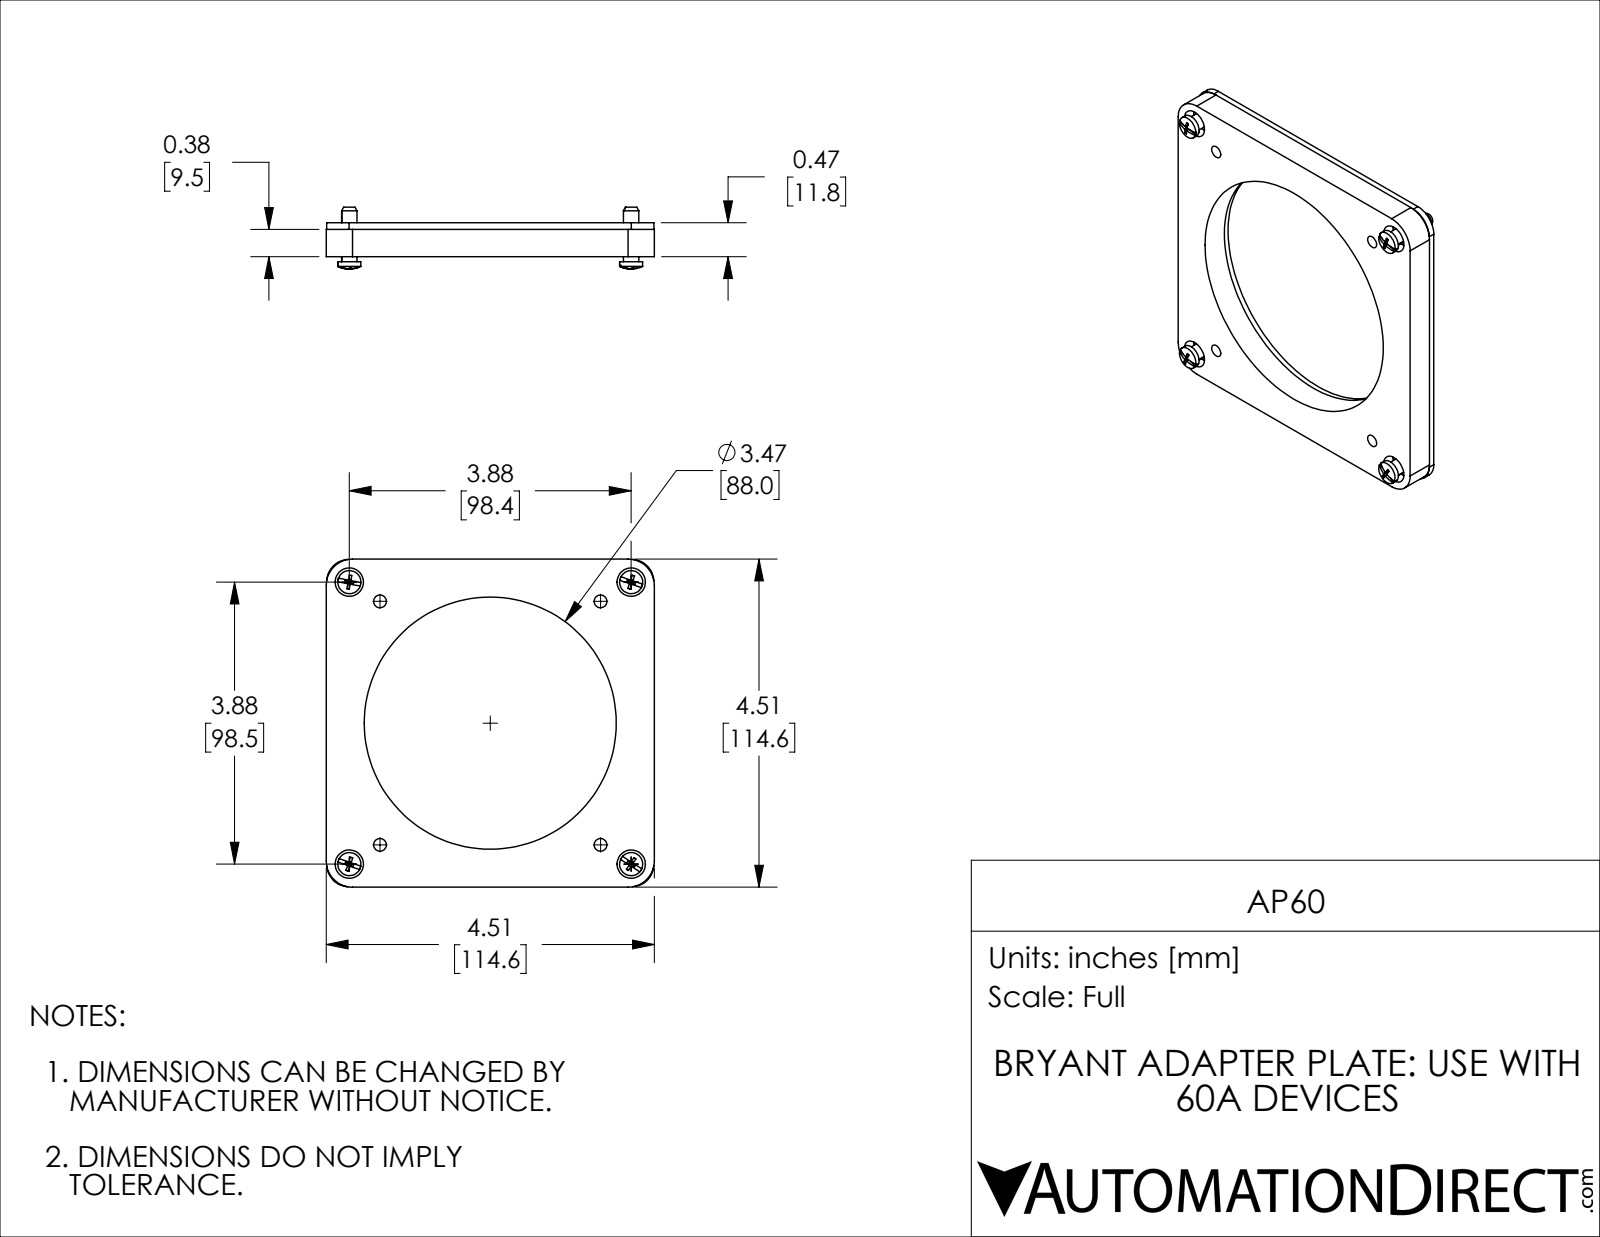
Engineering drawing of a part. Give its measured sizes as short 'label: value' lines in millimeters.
name: AP60
written by: SolidWorks 2021 (CONFIG_CONTROL_DESIGN)
unit: mm
bodies: 6 solids, 188 faces (100 planar, 72 cylindrical, 16 other)
size: 114.55 × 114.55 × 21.51
volume: 81 078 mm³; area: 39 036 mm²
holes: 8× ⌀5.49, 4× ⌀5.56, 4× ⌀9.91, 2× ⌀4.44, 2× ⌀4.45, 1× ⌀88.01, 1× ⌀88.9
bosses: 4× ⌀8.08, 4× ⌀5.38
rounds: 4× R7.87, 4× R9.14
face distances: 2.29, 11.81, 9.52, 114.56, 114.55, 114.43, 114.3, 114.42, 7.24, 4.95
hole spacings: 12.66, 69.59, 87.99, 92.34, 98.42, 98.43, 98.44, 98.45
